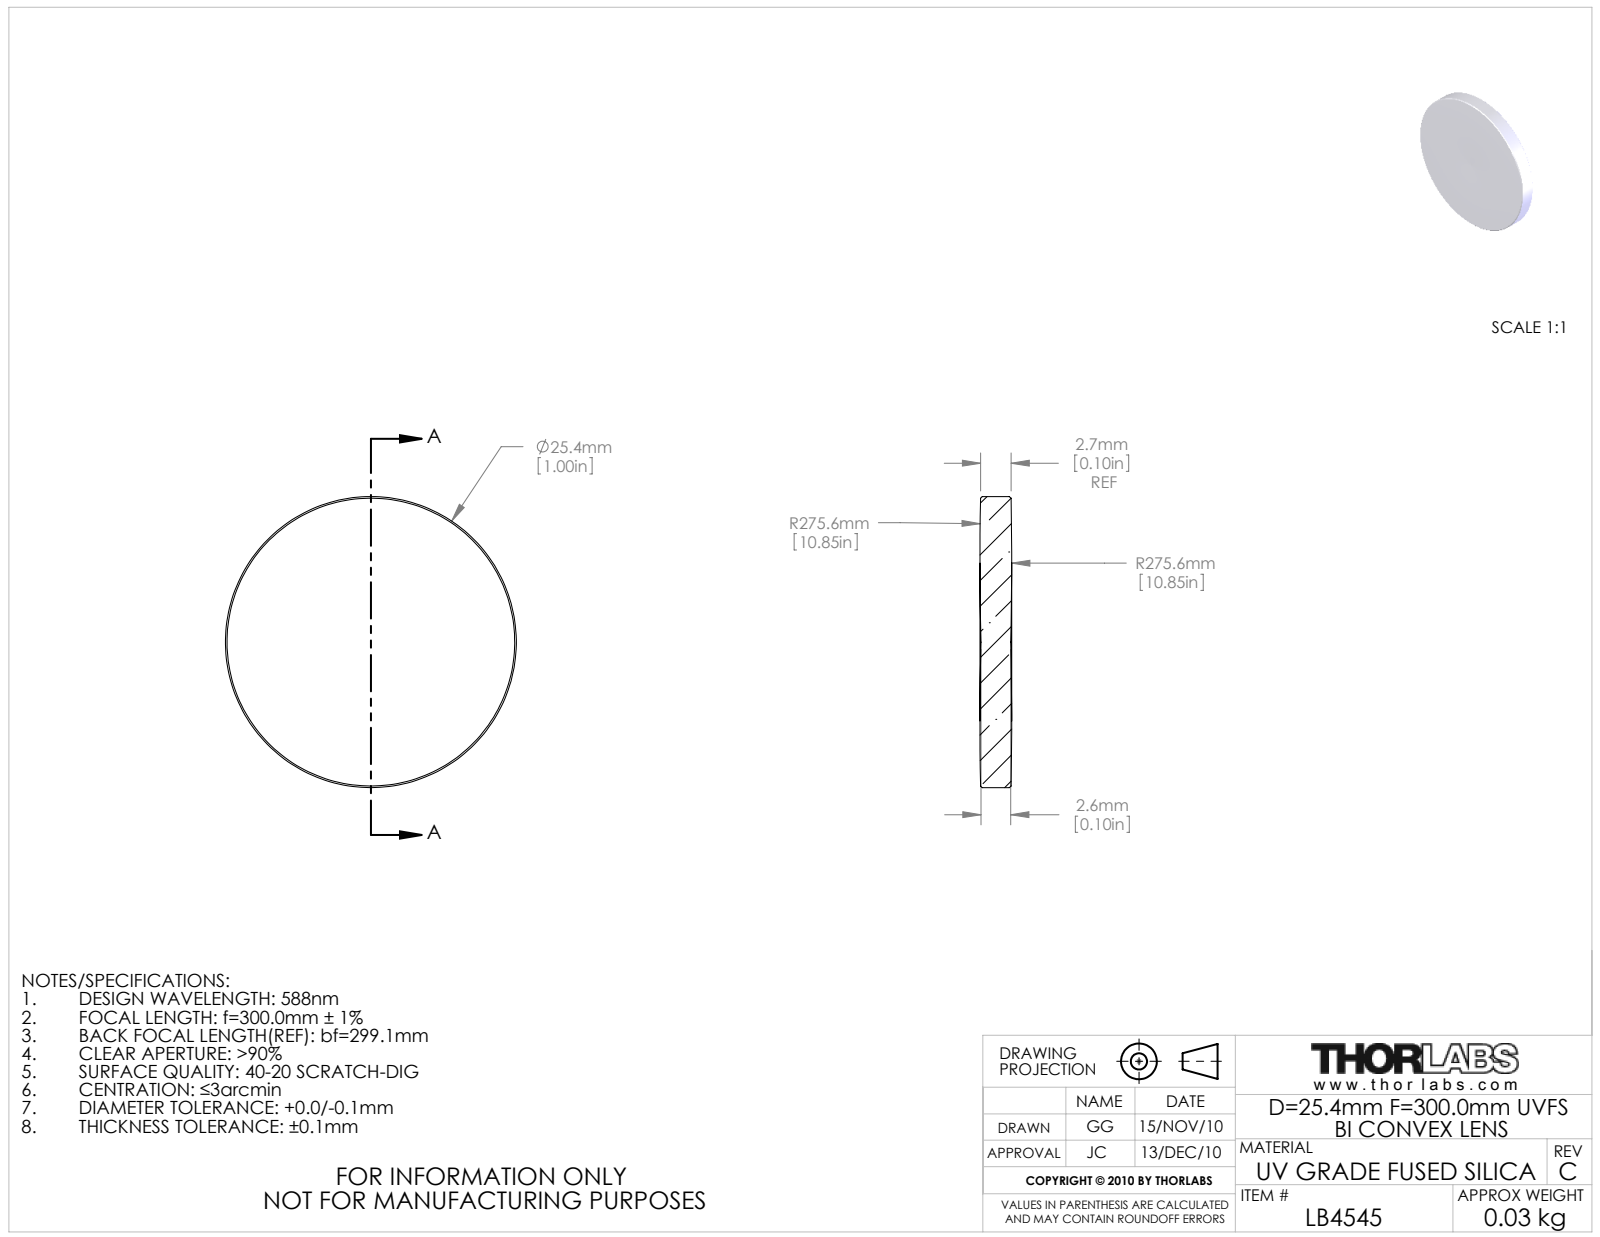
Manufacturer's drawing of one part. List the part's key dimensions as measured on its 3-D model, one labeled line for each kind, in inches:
Part name (STEP PRODUCT): 3409-E0W
STEP written by: SolidWorks 2009 (AUTOMOTIVE_DESIGN)
Units: inches
Bodies: 1 solid, 10 faces (0 planar, 2 cylindrical, 8 other)
Overall size (bounding box): 1 × 1 × 0.109
Volume: 0.084 in³ · Surface area: 1.879 in²
Round bosses / shafts (diameter × count): ⌀1 ×1
